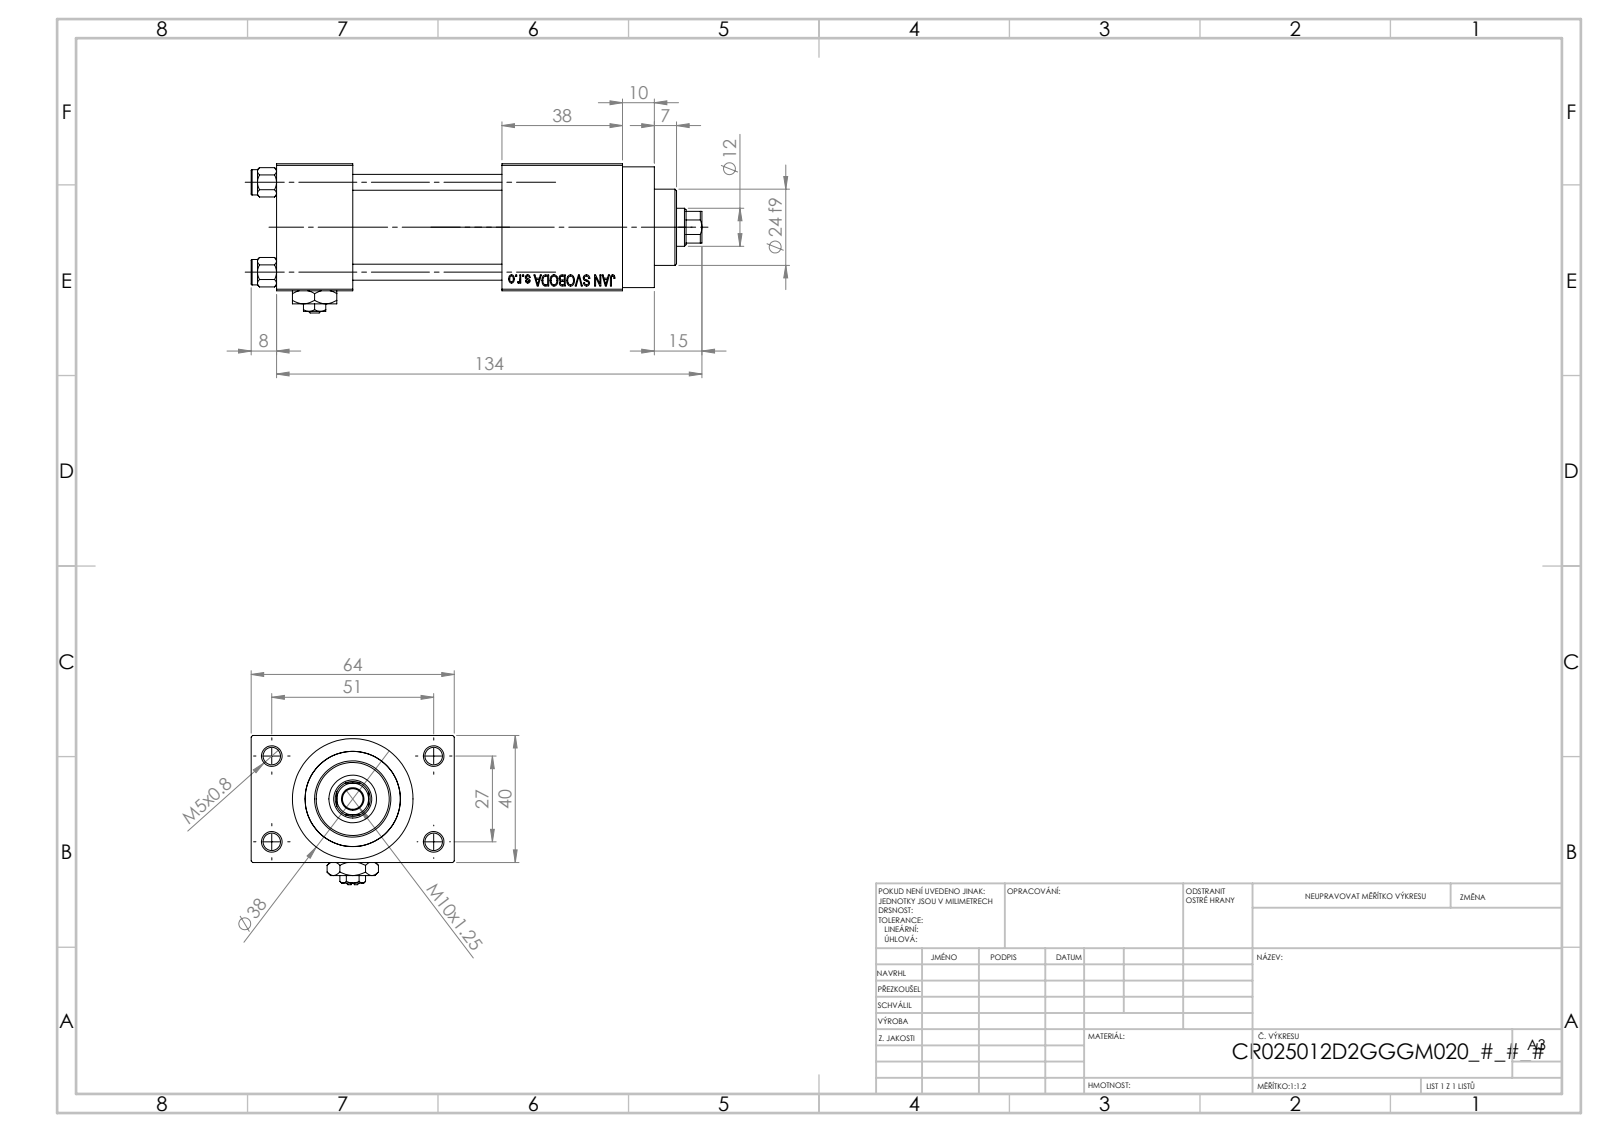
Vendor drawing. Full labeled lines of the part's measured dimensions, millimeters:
Part name (STEP PRODUCT): V215CR_D_TYCINKA; Zatka_pro_OIL_PORT; V215_VC_A; V215CR_VCP_D (+2 more)
STEP written by: SolidWorks 2019 (CONFIG_CONTROL_DESIGN)
Units: millimetres
Bodies: 12 solids, 1163 faces (521 planar, 100 cylindrical, 542 other)
Overall size (bounding box): 142 × 64 × 47
Volume: 174 001 mm³ · Surface area: 62 751 mm²
Round holes (diameter × count): ⌀5 ×4, ⌀5.5 ×4, ⌀20 ×3, ⌀2.5 ×2, ⌀7 ×2, ⌀13.16 ×2, ⌀6.5 ×1, ⌀12 ×1, ⌀15 ×1, ⌀25 ×1, ⌀30 ×1
Round bosses / shafts (diameter × count): ⌀8 ×4, ⌀38 ×1, ⌀31 ×1, ⌀24 ×1
Partial cylindrical surfaces — rounded edges, fillets, slot ends (radius × count): R5.5 ×1
Main face-to-face distances: 40, 52, 12, 47, 24, 71, 64, 38, 109, 85
Hole centre spacings: 11.37, 14.18, 18.23, 20.01, 28.3, 28.85, 29.89, 30.84
